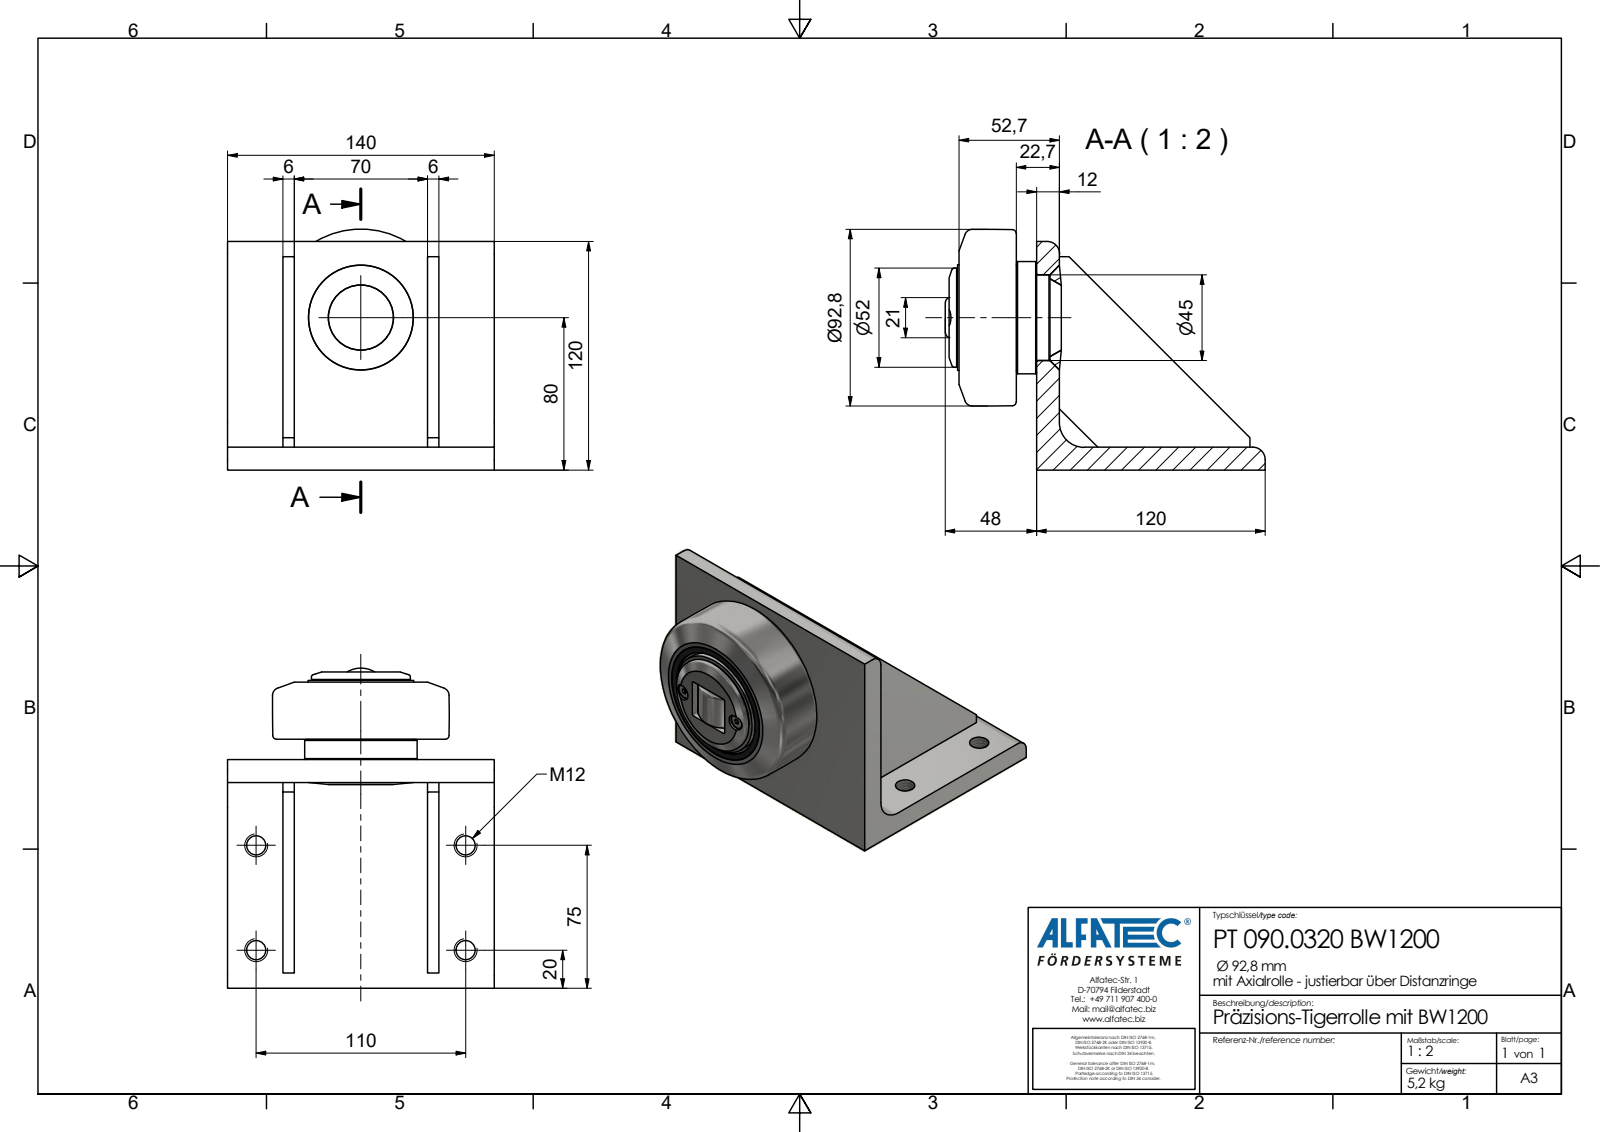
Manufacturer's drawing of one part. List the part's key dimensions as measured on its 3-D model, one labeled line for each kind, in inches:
Part name (STEP PRODUCT): PT 090.0320 BW1200_Kontur
STEP written by: Autodesk Inventor 2020 (AP242_MANAGED_MODEL_BASED_3D_ENGINEERING_MIM_LF)
Units: inches
Bodies: 1 solid, 97 faces (57 planar, 25 cylindrical, 15 other)
Overall size (bounding box): 6.614 × 5.512 × 4.976
Volume: 41.61 in³ · Surface area: 175.1 in²
Round holes (diameter × count): ⌀0.398 ×4, ⌀0.339 ×2
Round bosses / shafts (diameter × count): ⌀0.307 ×2, ⌀2.323 ×1, ⌀2.185 ×1, ⌀2.177 ×1, ⌀2.047 ×1
Partial cylindrical surfaces — rounded edges, fillets, slot ends (radius × count): R0.039 ×4, R0.256 ×2, R0.315 ×1, R0.354 ×1, R0.413 ×1, R0.512 ×1
Main face-to-face distances: 0.472, 2.992, 0.236, 1.142, 1.378, 4.134, 4.37, 3.228, 2.756, 0.421
Hole centre spacings: 2.165, 4.331, 4.842, 1.535
